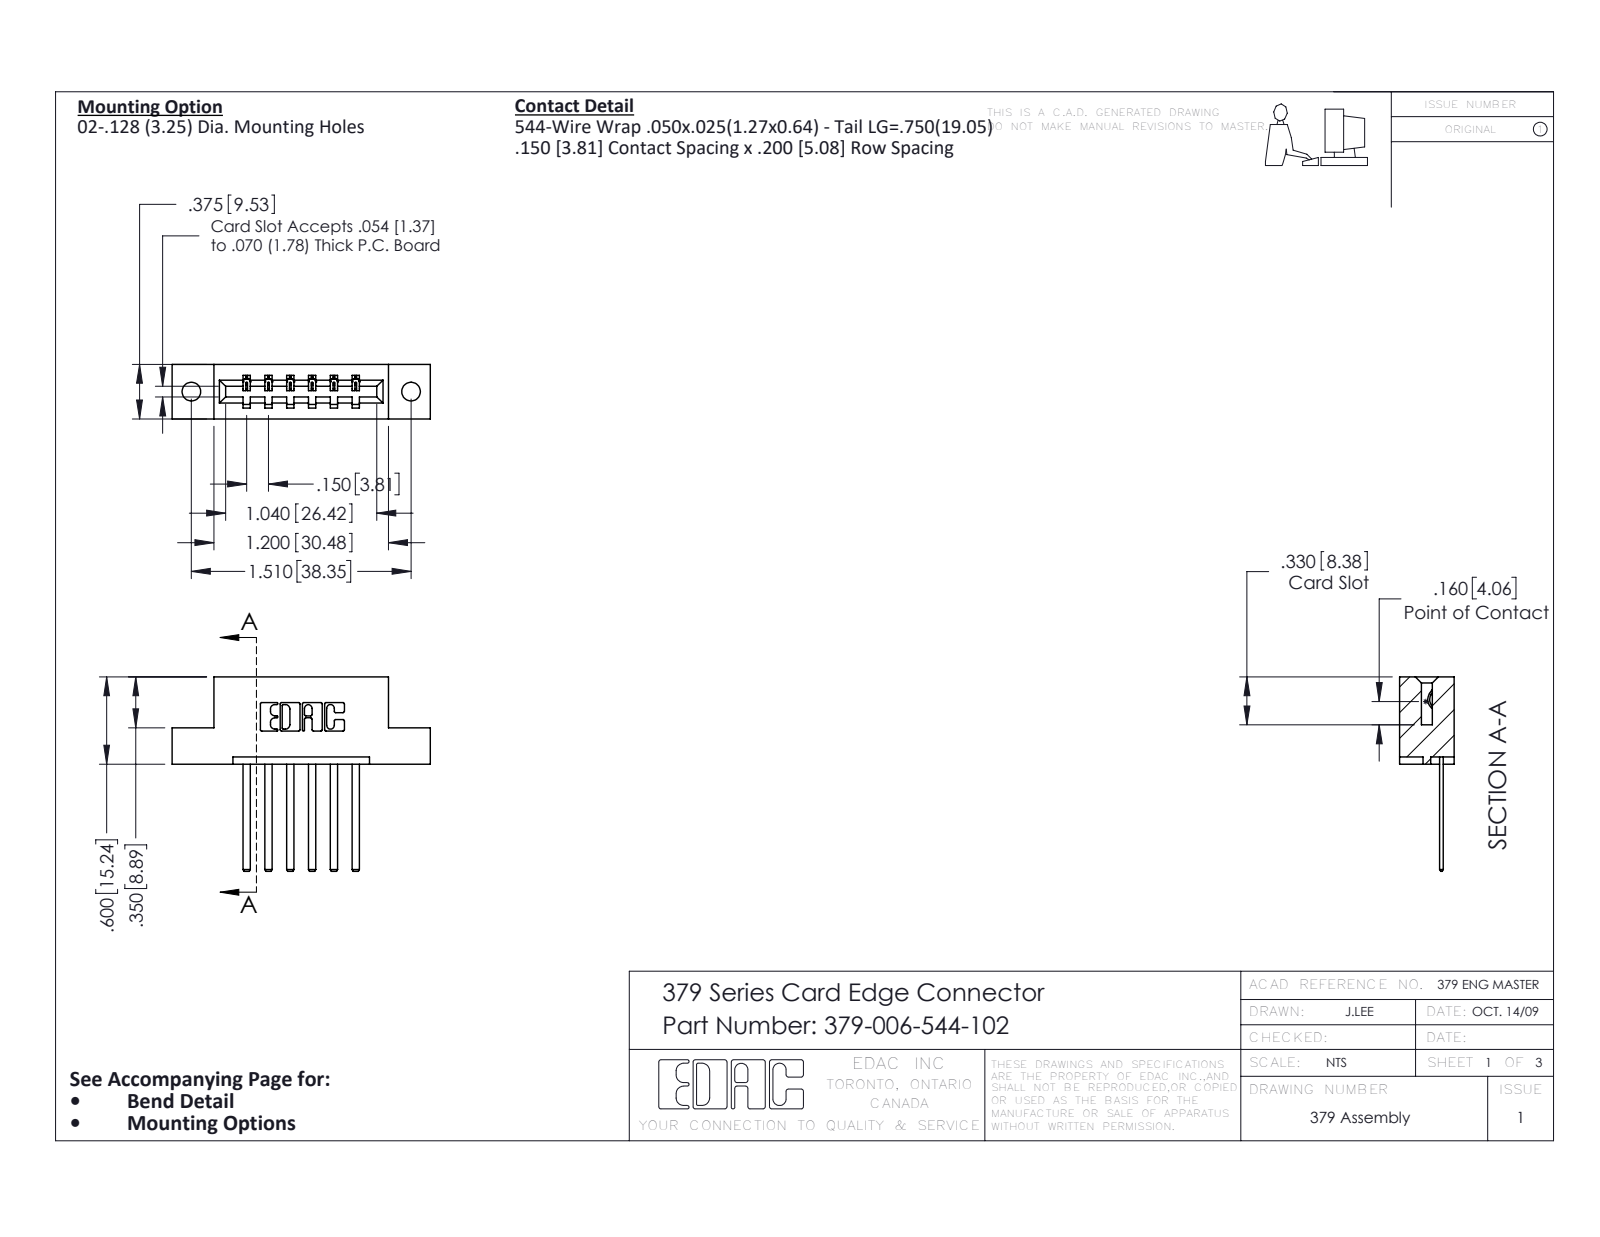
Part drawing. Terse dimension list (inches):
name: 345-292-001_345-293-144; 379 Part_Flush - .128 Dia; 379-006-544-102
written by: SolidWorks 2016 (CONFIG_CONTROL_DESIGN)
unit: in
bodies: 7 solids, 426 faces (298 planar, 128 cylindrical, 0 other)
size: 1.775 × 1.337 × 0.375
volume: 0.265 in³; area: 6.543 in²
holes: 2× ⌀0.128
rounds: 22× R0.01, 12× R0.006, 6× R0.007, 6× R0.031, 3× R0.026, 1× R0.014, 1× R0.022, 1× R0.024
face distances: 0.3, 0.2, 0.15, 0.1, 0.05, 0.075, 0.375, 0.35, 0.25, 0.6
hole spacings: 1.51
